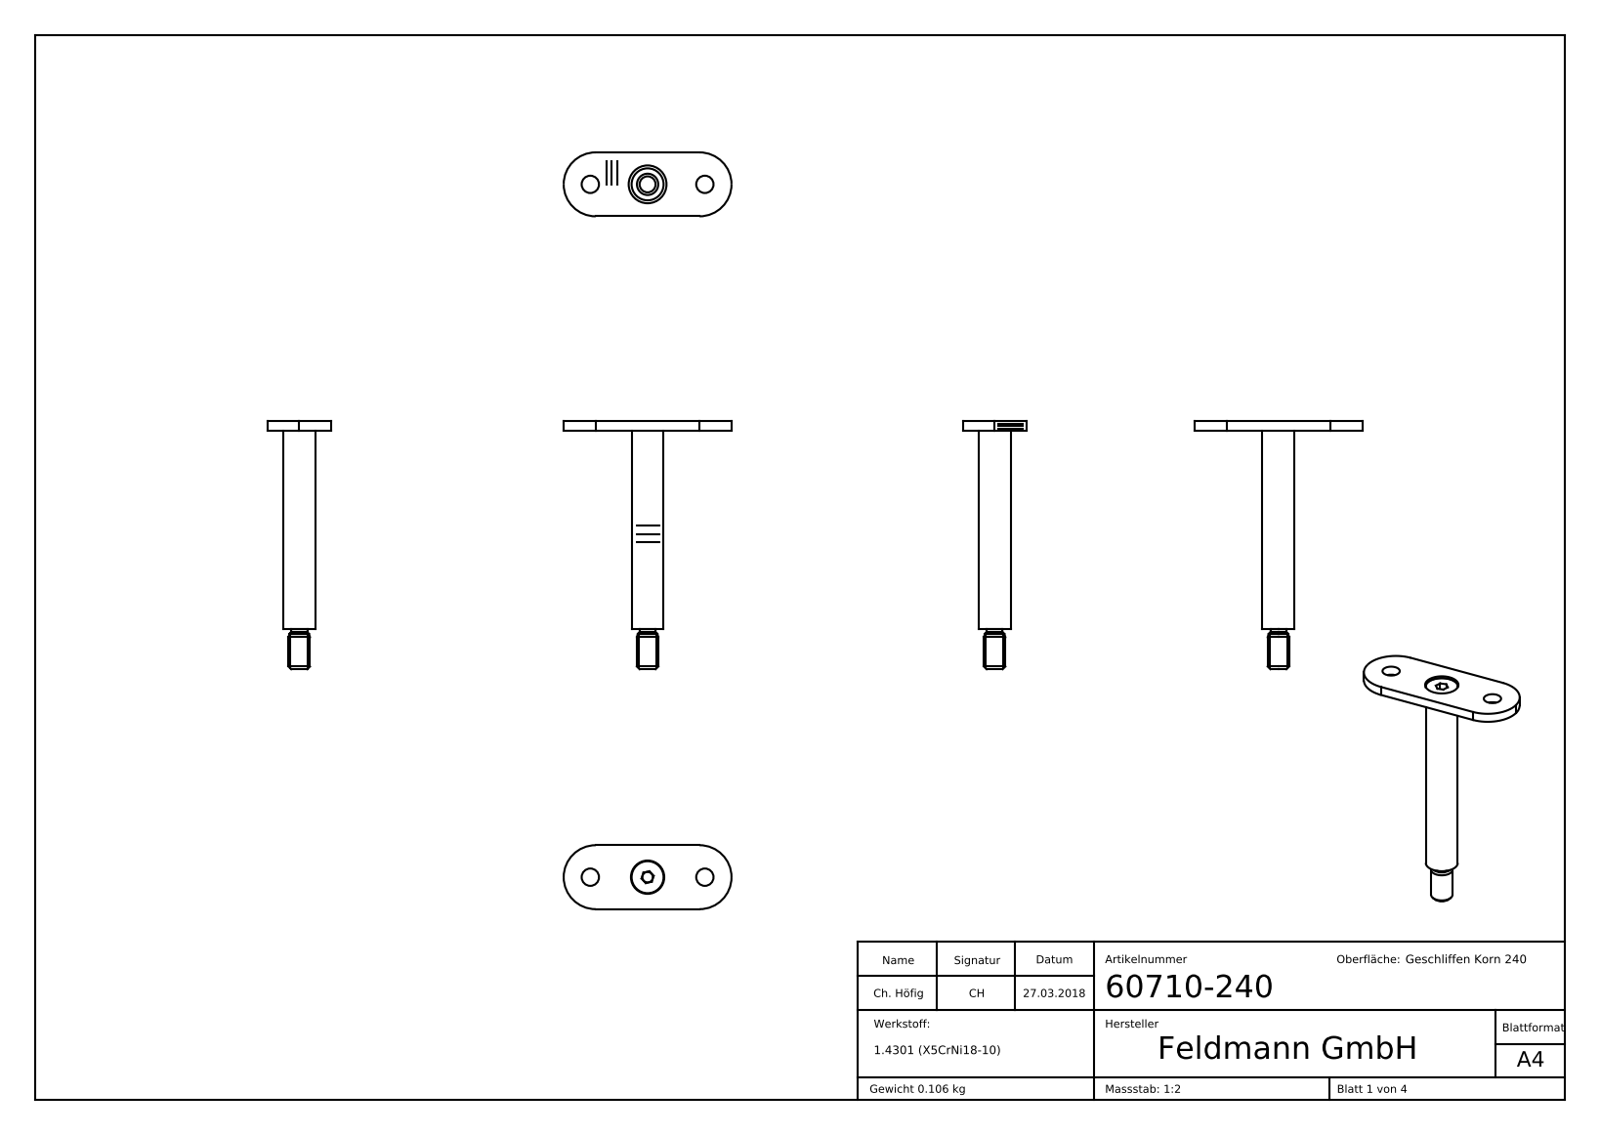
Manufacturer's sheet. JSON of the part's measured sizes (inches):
{"part_name": "60710-240; 60180-240; DIN-7991_-_DIN7991 M6x16_DIN7991 M6x12; 50236-Konfig_50236-240-75-M6 (+3 more)", "step_written_by": "SolidWorks 2018 (CONFIG_CONTROL_DESIGN)", "units": "inches", "bodies": {"solids": 3, "faces": 256, "planar": 138, "cylindrical": 14, "other": 104}, "overall_size": [3.701, 2.48, 0.945], "volume_in3": 1.004, "surface_area_in2": 12.51, "round_holes": [[0.256, 2], [0.197, 1], [0.492, 1], [0.559, 1]], "round_bosses_or_shafts": [[0.551, 1], [0.472, 1], [0.315, 1], [0.236, 1]], "partial_cylinders_radius": [[0.472, 2]], "face_to_face_distances": [0.138, 0.118, 0.02, 0.945, 0.028, 0.11, 0.091, 3.524, 3.543, 3.634], "hole_center_spacings": [0.846, 1.693]}
